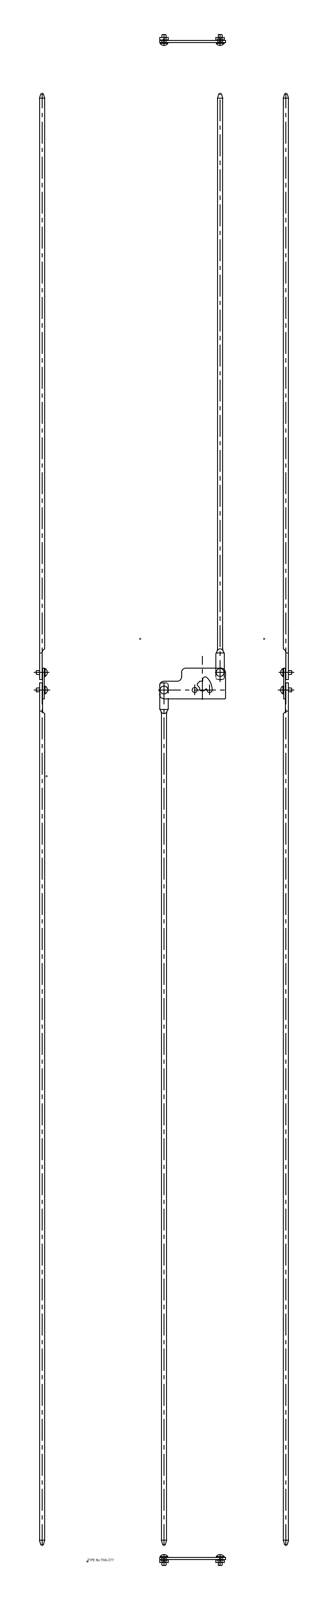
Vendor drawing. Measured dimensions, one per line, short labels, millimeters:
name: cam; rod(A); rod(B)
written by: spGate 19.8.4 (****-****-****-****) (AUTOMOTIVE_DESIGN)
unit: mm
bodies: 3 solids, 94 faces (35 planar, 43 cylindrical, 16 other)
size: 1655 × 75 × 12.5
volume: 51 229 mm³; area: 36 370 mm²
holes: 2× ⌀5.2, 1× ⌀5.8
bosses: 2× ⌀9, 2× ⌀6, 2× ⌀4.8, 2× ⌀3.8
rounds: 7× R2, 5× R5, 3× R0.5, 2× R1, 2× R2.9, 1× R5.9, 1× R19.9
face distances: 2.3, 0.4, 2.7, 5.7, 3.4, 3, 64, 9.4, 3.1, 6.1
hole spacings: 35, 35.23, 67.05
